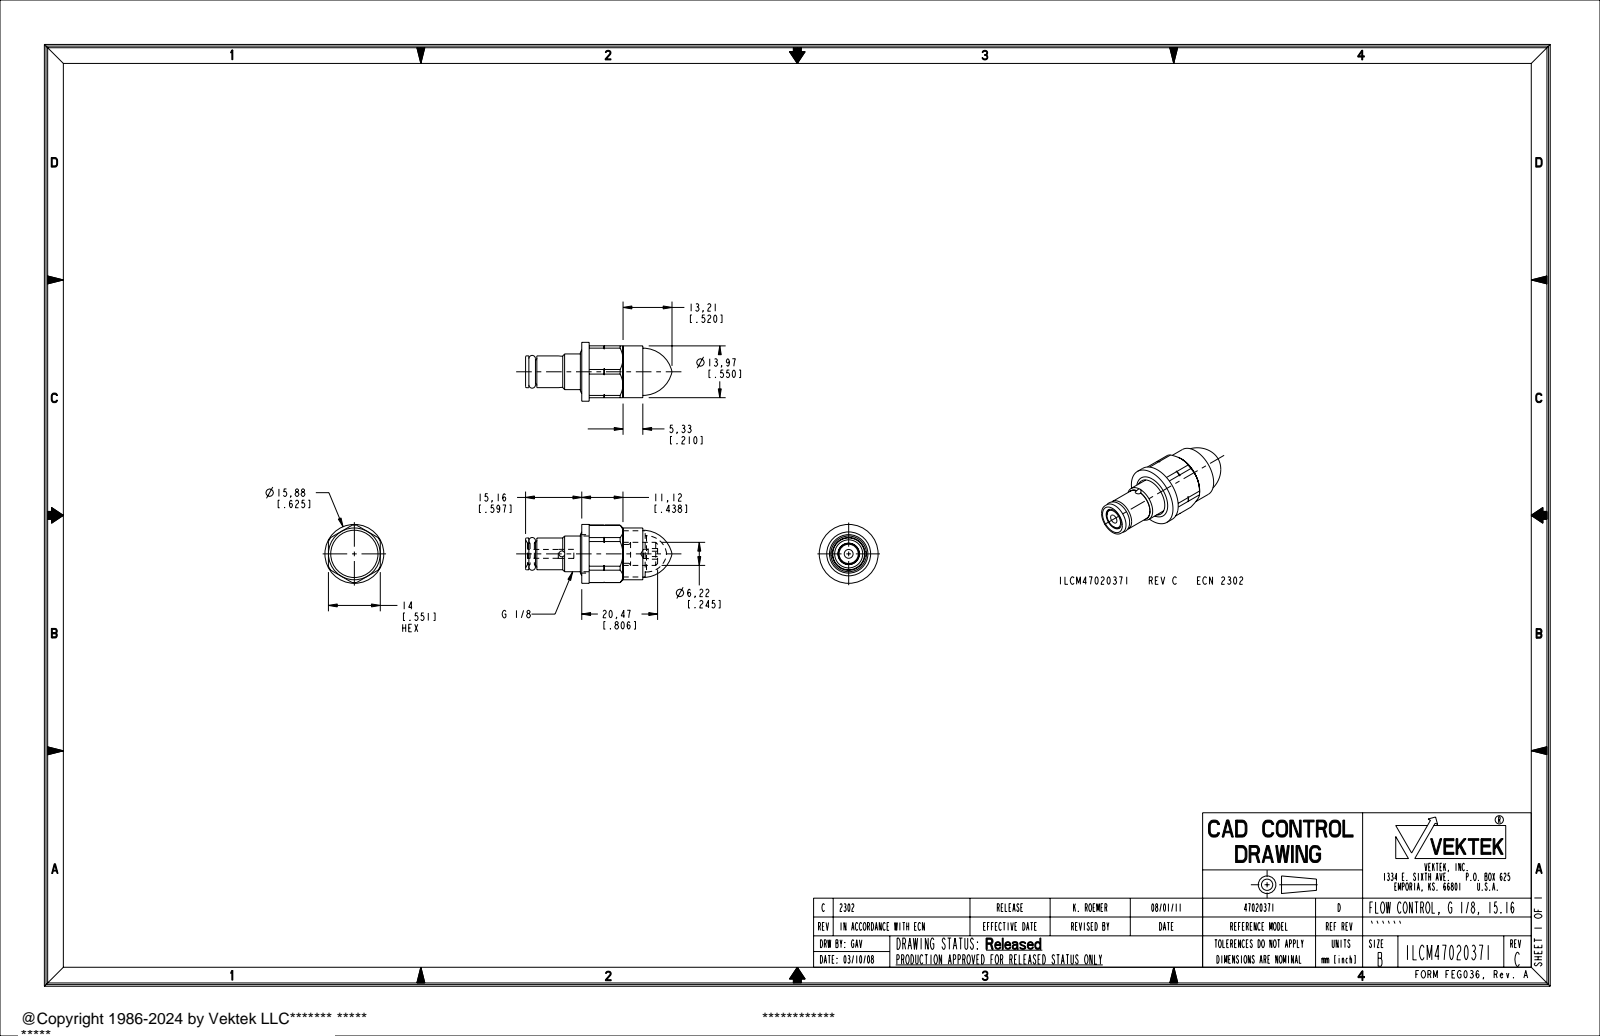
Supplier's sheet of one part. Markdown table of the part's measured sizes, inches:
| quantity | value |
| --- | --- |
| part name | ILCM47020371 |
| STEP written by | PRO/ENGINEER BY PARAMETRIC TECHNOLOGY CORPORATION, 2007460 (AUTOMOTIVE_DESIGN_CC2) |
| units | inches |
| bodies | 3 solids, 125 faces (41 planar, 44 cylindrical, 40 other) |
| overall size | 1.556 × 0.625 × 0.625 |
| volume | 0.217 in³ |
| surface area | 4.58 in² |
| round holes (diameter × count) | 0.062 × 1, 0.094 × 1, 0.096 × 1, 0.098 × 1, 0.228 × 1, 0.386 × 1, 0.408 × 1 |
| round bosses / shafts (diameter × count) | 0.625 × 1, 0.55 × 1, 0.379 × 1, 0.338 × 1, 0.337 × 1, 0.245 × 1, 0.224 × 1, 0.2 × 1 |
| partial cylindrical surfaces (radius × count) | 0.305 × 1 |
| main face-to-face distances | 0.063, 0.488, 0.551, 0.425, 0.438, 0.439, 0.36, 0.359, 0.079, 1 |
